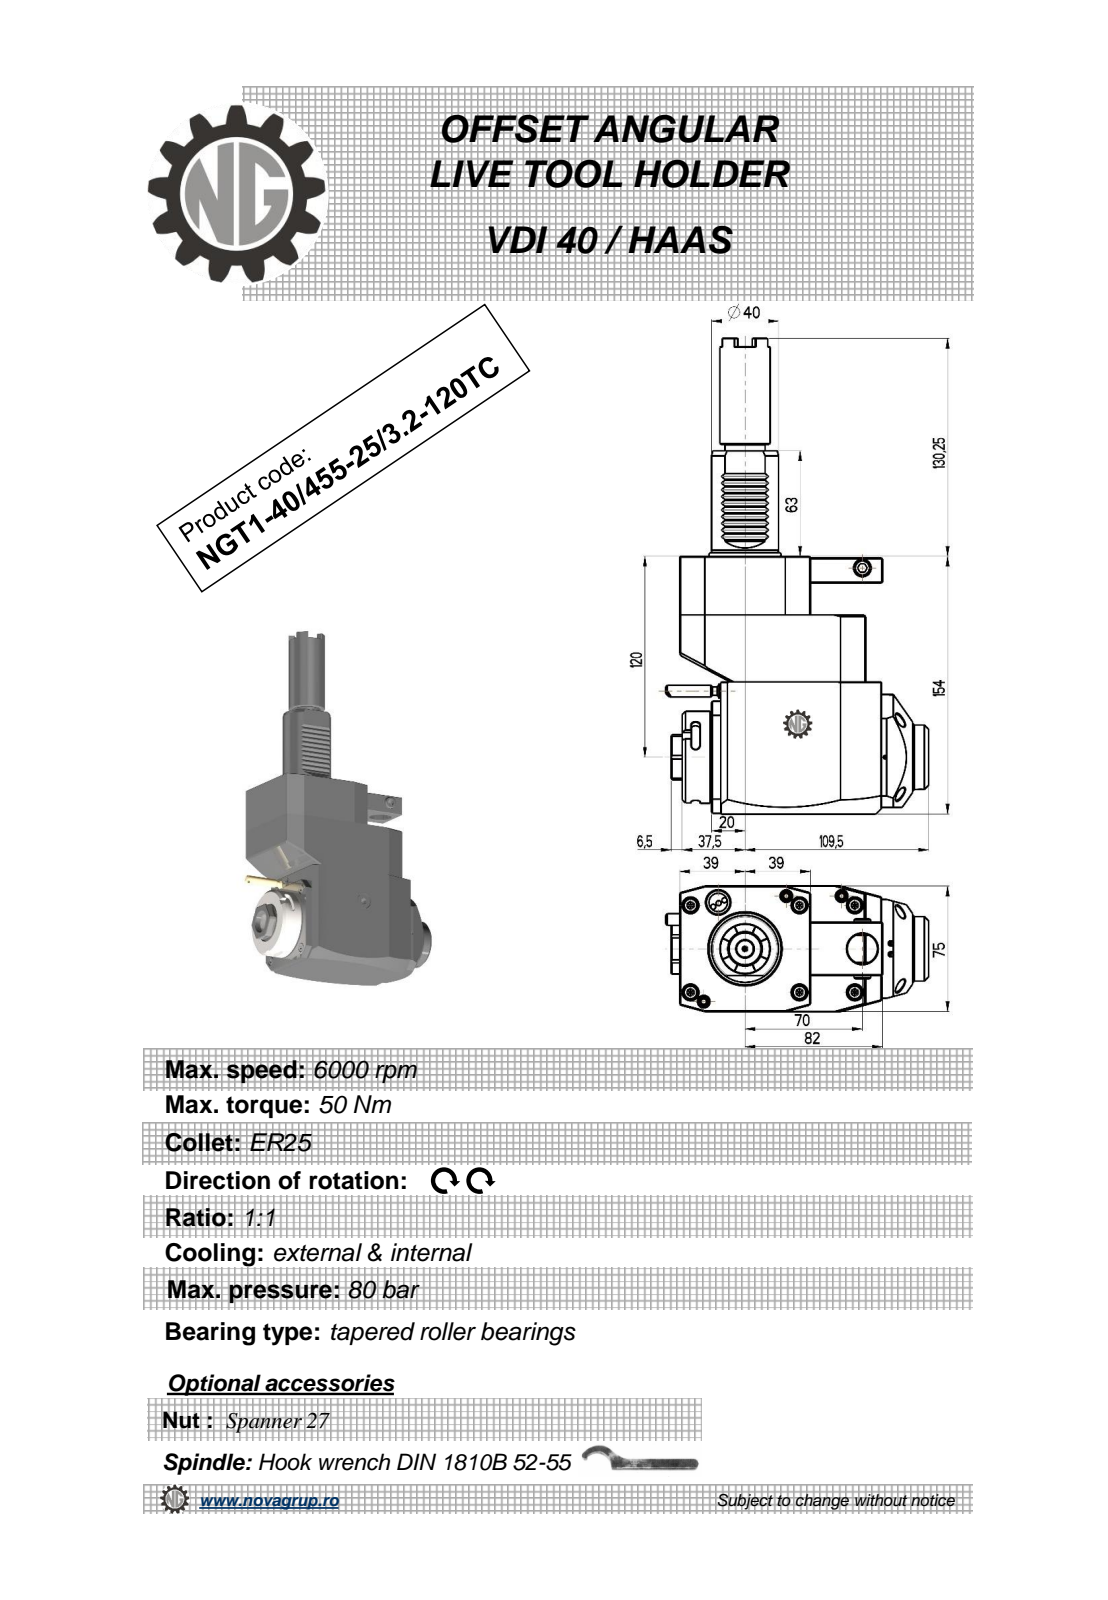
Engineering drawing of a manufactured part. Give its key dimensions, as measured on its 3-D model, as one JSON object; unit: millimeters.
{"part_name": "NGT1_40_455_25_3_2_120TC", "step_written_by": "PRO/ENGINEER BY PARAMETRIC TECHNOLOGY CORPORATION, 2010280 (CONFIG_CONTROL_DESIGN)", "units": "millimeters", "bodies": {"solids": 1, "faces": 374, "planar": 216, "cylindrical": 72, "other": 86}, "overall_size": [284.25, 156.83, 75], "volume_mm3": 1325000, "surface_area_mm2": 98134, "round_holes": [[18, 2], [2.5, 1], [3, 1], [9.5, 1], [20, 1]], "round_bosses_or_shafts": [[8.96, 2], [55, 1], [48, 1], [40, 1], [38.5, 1], [30, 1], [24, 1], [10, 1]], "partial_cylinders_radius": [[0.3, 10], [2.5, 6], [180, 2], [0.5, 1], [4.25, 1], [15, 1], [24.5, 1], [37.5, 1]], "face_to_face_distances": [75, 154, 19, 119, 59, 111, 92, 35, 17.5, 53.5], "hole_center_spacings": [43.2, 70, 75.07, 112.5]}
